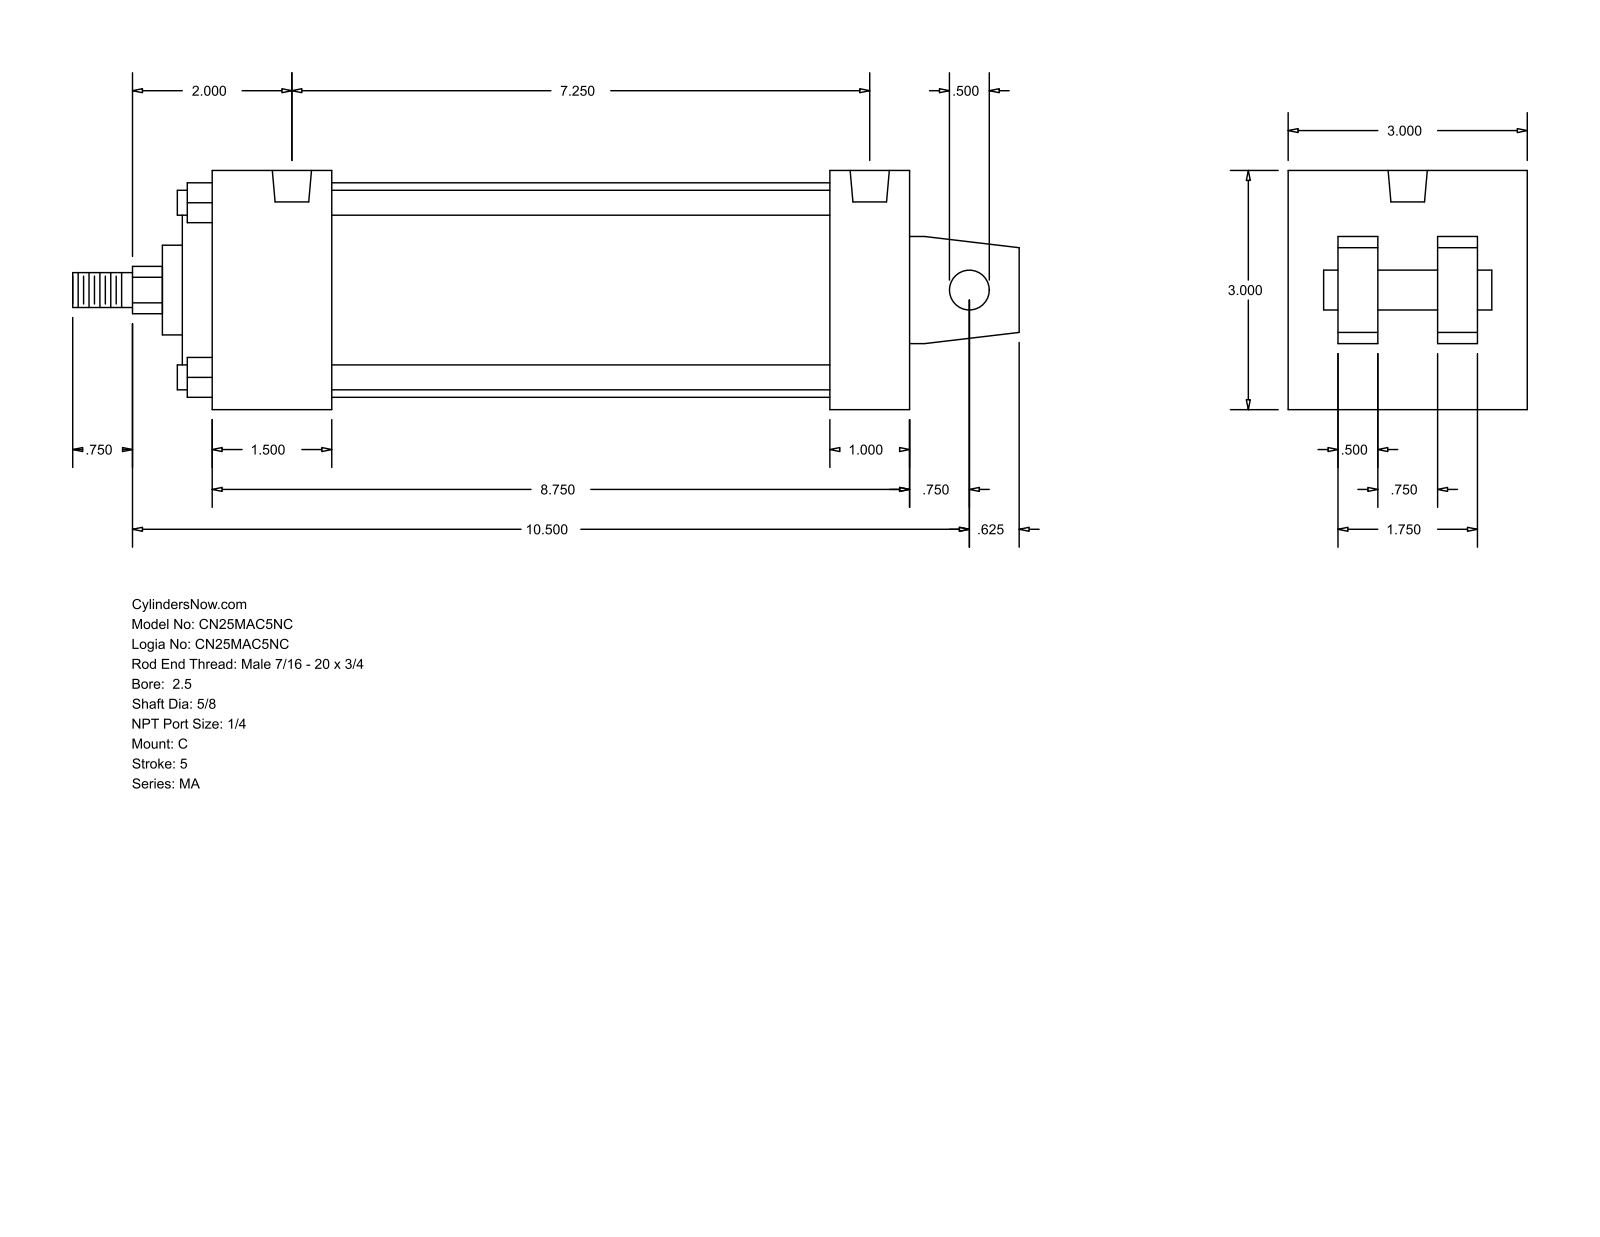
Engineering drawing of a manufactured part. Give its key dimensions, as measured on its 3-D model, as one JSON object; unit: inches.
{"part_name": "MA_C__0250_0.625", "step_written_by": "GSSL Pune (CONFIG_CONTROL_DESIGN)", "units": "inches", "bodies": {"solids": 0, "faces": 105, "planar": 77, "cylindrical": 28, "other": 0}, "overall_size": [11.875, 3, 3], "round_holes": [[0.313, 4], [0.492, 2]], "round_bosses_or_shafts": [[0.313, 4], [2.69, 1], [2, 1], [1.125, 1], [0.625, 1], [0.5, 1], [0.437, 1]], "partial_cylinders_radius": [[0.297, 1]], "face_to_face_distances": [3, 8.75, 0.5, 0.625, 1.875, 1, 1.5, 7.75, 6.25, 7.25], "hole_center_spacings": [7.25]}
